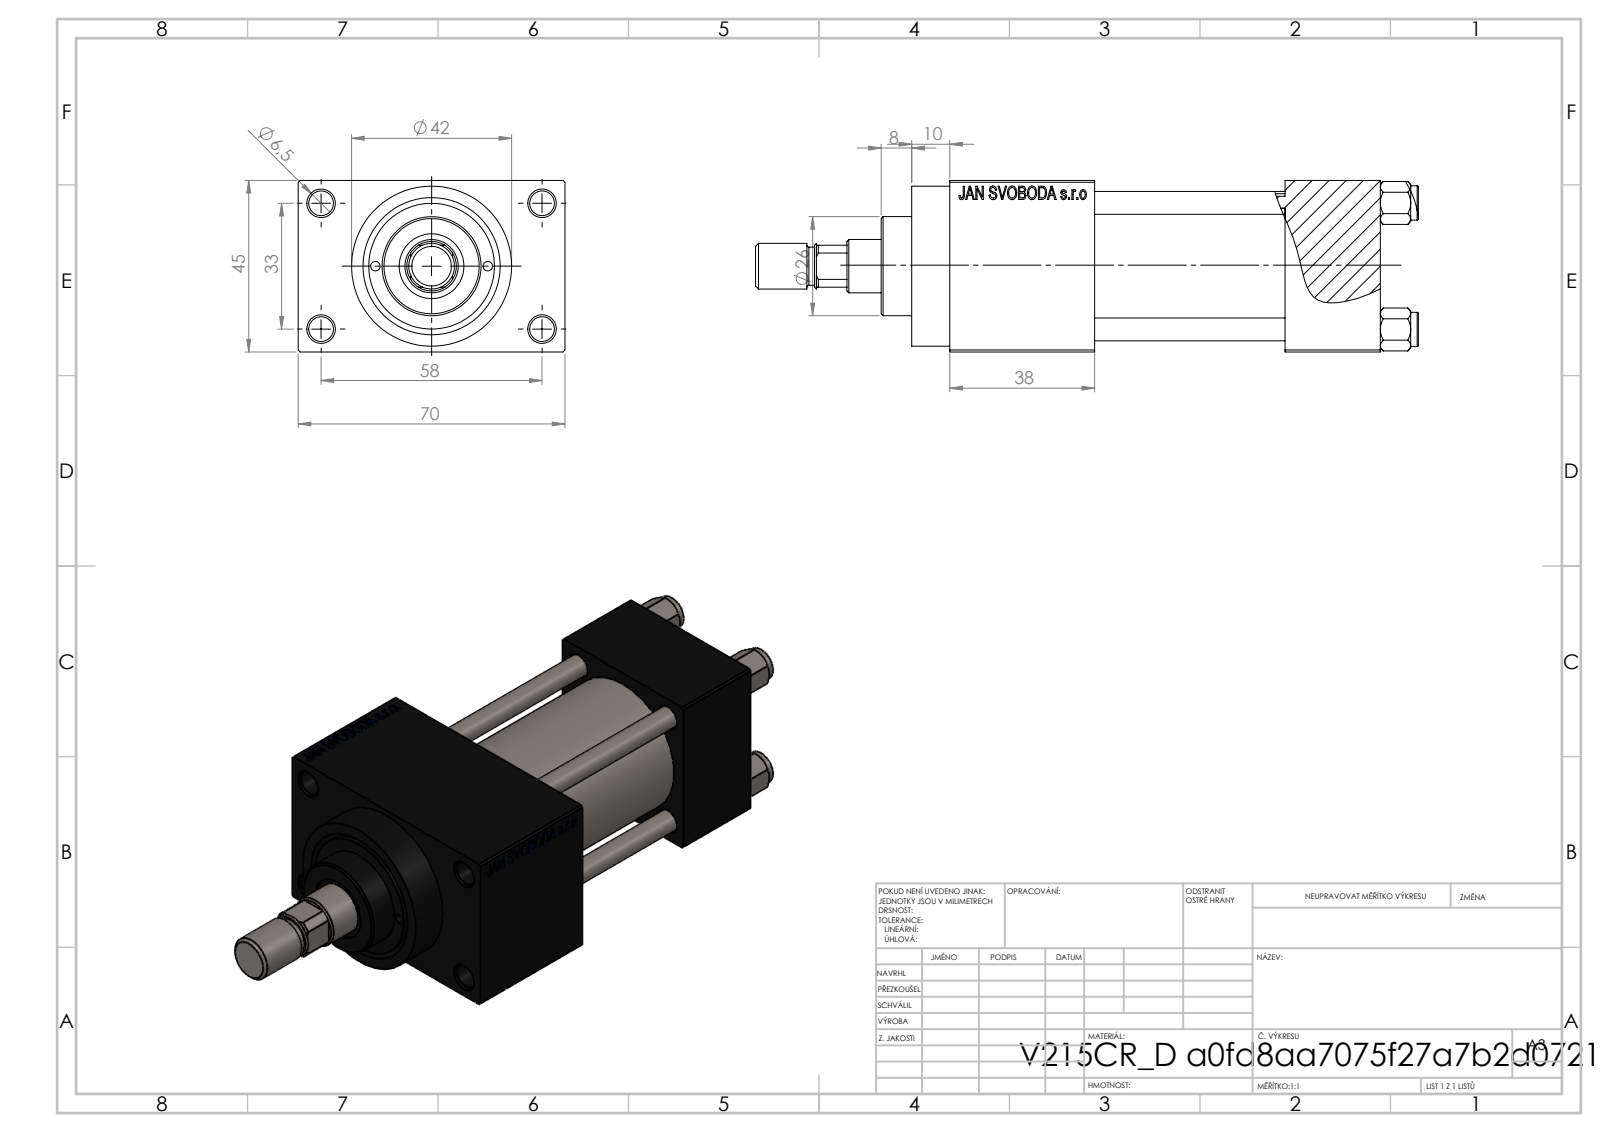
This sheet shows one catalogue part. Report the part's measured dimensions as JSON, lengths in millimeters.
{"part_name": "NUT_M5_D; V215CR_D_Body; V215CR_D_TYCINKA; ROD_END_AH (+2 more)", "step_written_by": "SolidWorks 2019 (CONFIG_CONTROL_DESIGN)", "units": "millimeters", "bodies": {"solids": 12, "faces": 1124, "planar": 502, "cylindrical": 96, "other": 526}, "overall_size": [174, 70, 45], "volume_mm3": 231884, "surface_area_mm2": 76228, "round_holes": [[6.5, 5], [6, 4], [2.5, 2], [7, 2], [13.16, 2], [20, 2], [14, 1], [17, 1], [24, 1], [32, 1], [33, 1]], "round_bosses_or_shafts": [[9, 4], [42, 1], [38, 1], [26, 1], [12, 1], [10, 1]], "partial_cylinders_radius": [[6.5, 1]], "face_to_face_distances": [45, 25, 50, 12.5, 75, 57.5, 88, 38, 113, 70], "hole_center_spacings": [12.4, 16.7, 21.8, 23.48, 33.2, 33.37, 35.35, 35.47]}
